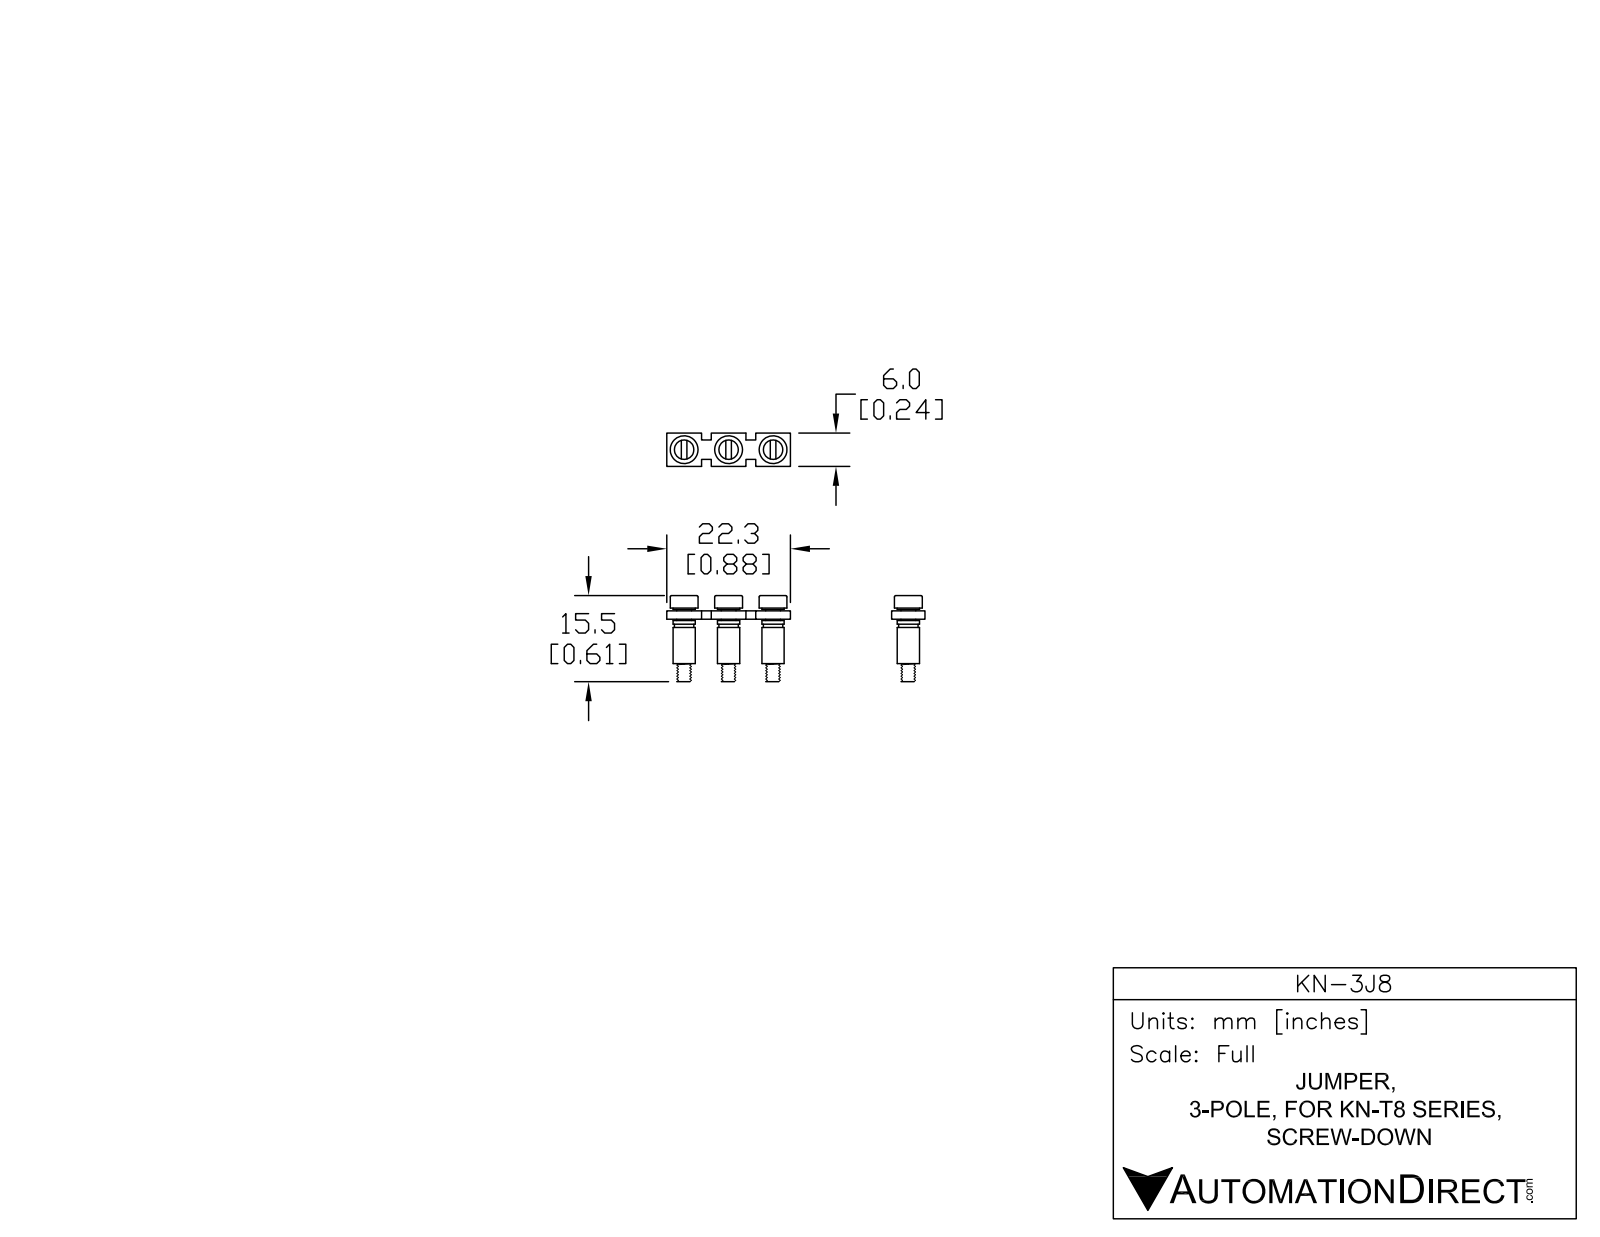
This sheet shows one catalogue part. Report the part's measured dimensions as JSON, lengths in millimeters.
{"part_name": "KN-3J8", "step_written_by": "SolidWorks 2014 (AUTOMOTIVE_DESIGN)", "units": "millimeters", "bodies": {"solids": 10, "faces": 151, "planar": 70, "cylindrical": 63, "other": 18}, "overall_size": [22.25, 15.5, 6], "volume_mm3": 606, "surface_area_mm2": 1667, "round_holes": [[2.8, 3], [3, 3], [3.15, 3], [3.5, 3]], "round_bosses_or_shafts": [[5, 3], [4, 3], [2.65, 3]], "face_to_face_distances": [1.5, 2, 1.75, 2.25, 0.5, 8, 1, 1.25, 2.75, 6], "hole_center_spacings": [8, 16]}
